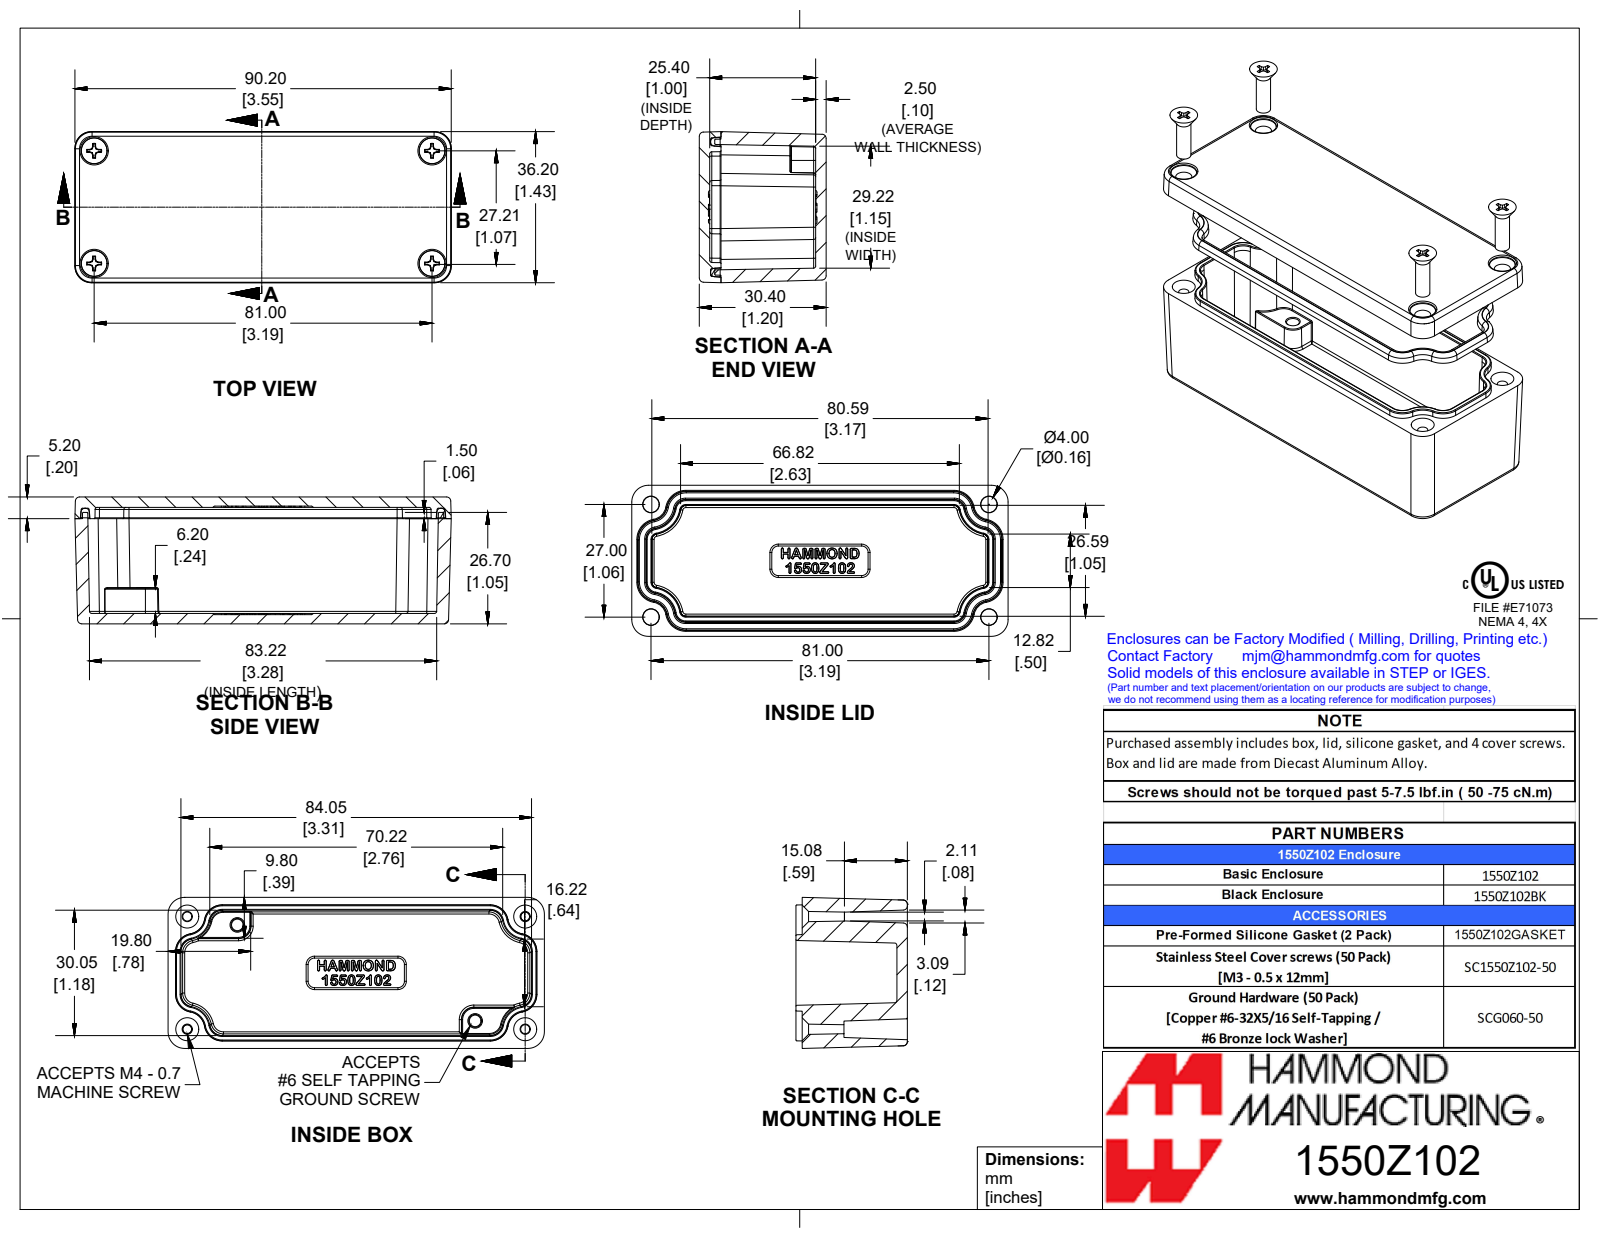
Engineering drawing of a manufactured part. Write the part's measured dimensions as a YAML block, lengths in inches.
part_name: "1550Z102"
step_written_by: "SolidWorks 2019 (AUTOMOTIVE_DESIGN)"
units: inches
bodies: {solids: 7, faces: 1214, planar: 314, cylindrical: 88, other: 812}
overall_size: [3.551, 1.425, 1.199]
volume: 2.385
surface_area: 46.94
round_bosses_or_shafts:
  - {diameter: 0.22, count: 4}
  - {diameter: 0.102, count: 4}
partial_cylinders:
  - {radius: 0.008, count: 28}
  - {radius: 0.02, count: 20}
  - {radius: 0.039, count: 16}
  - {radius: 0.012, count: 8}
  - {radius: 0.157, count: 8}
face_to_face_distances: [0.098, 1.098, 1.197, 0.992, 0.106, 1, 0.894, 0.205, 1.425, 0.118]
